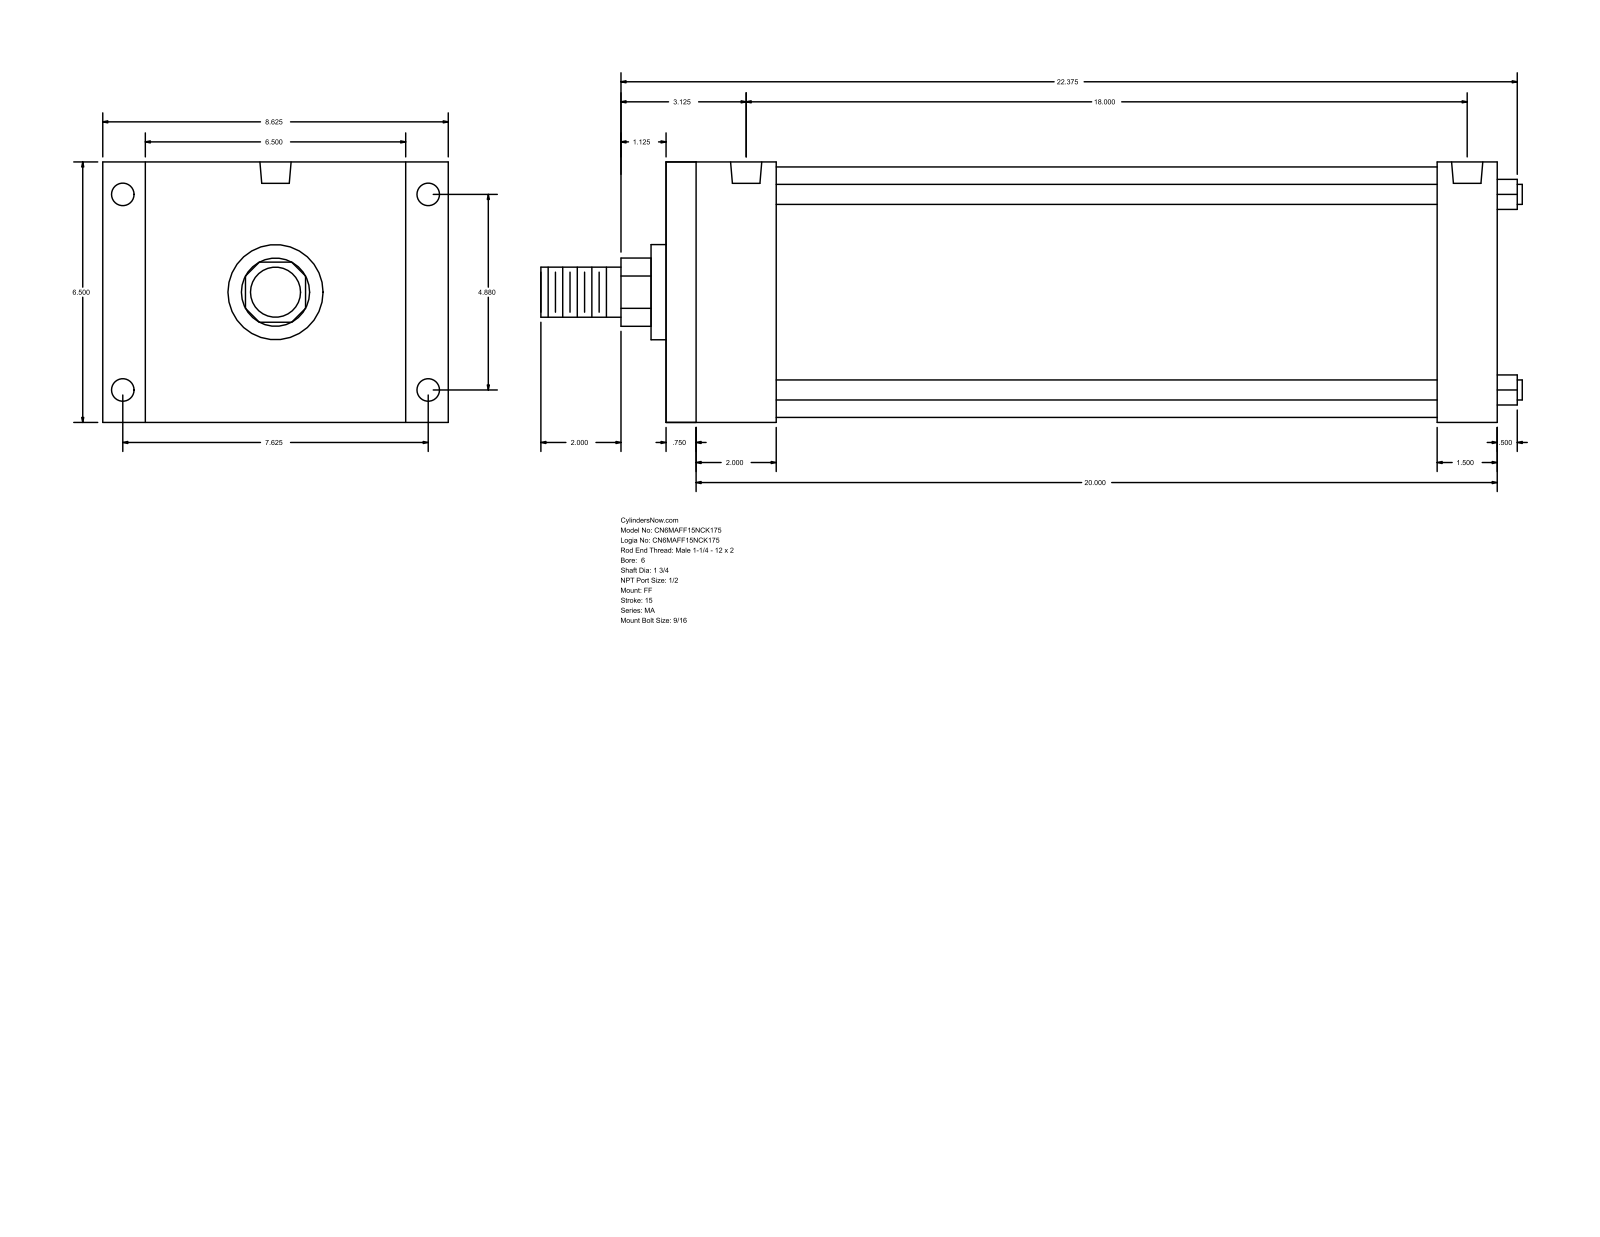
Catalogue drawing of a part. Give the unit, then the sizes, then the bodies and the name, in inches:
Units: inches
Overall size (bounding box): 24.5 × 8.625 × 6.5
Round holes (diameter × count): ⌀0.563 ×4, ⌀0.687 ×4, ⌀0.778 ×2
Round bosses / shafts (diameter × count): ⌀0.5 ×4, ⌀6.25 ×1, ⌀2.375 ×1, ⌀1.75 ×1, ⌀1.25 ×1
Partial cylindrical surfaces — rounded edges, fillets, slot ends (radius × count): R0.852 ×1
Main face-to-face distances: 6.5, 20.75, 0.75, 20, 2.75, 1.5, 2, 18, 19.25, 18.5
Hole centre spacings: 4.88, 7.625, 9.053, 18
Bodies: 0 solids, 92 faces (64 planar, 28 cylindrical, 0 other)
Part name (STEP PRODUCT): MA_FF__0600_1.75
STEP written by: GSSL Pune (CONFIG_CONTROL_DESIGN)
